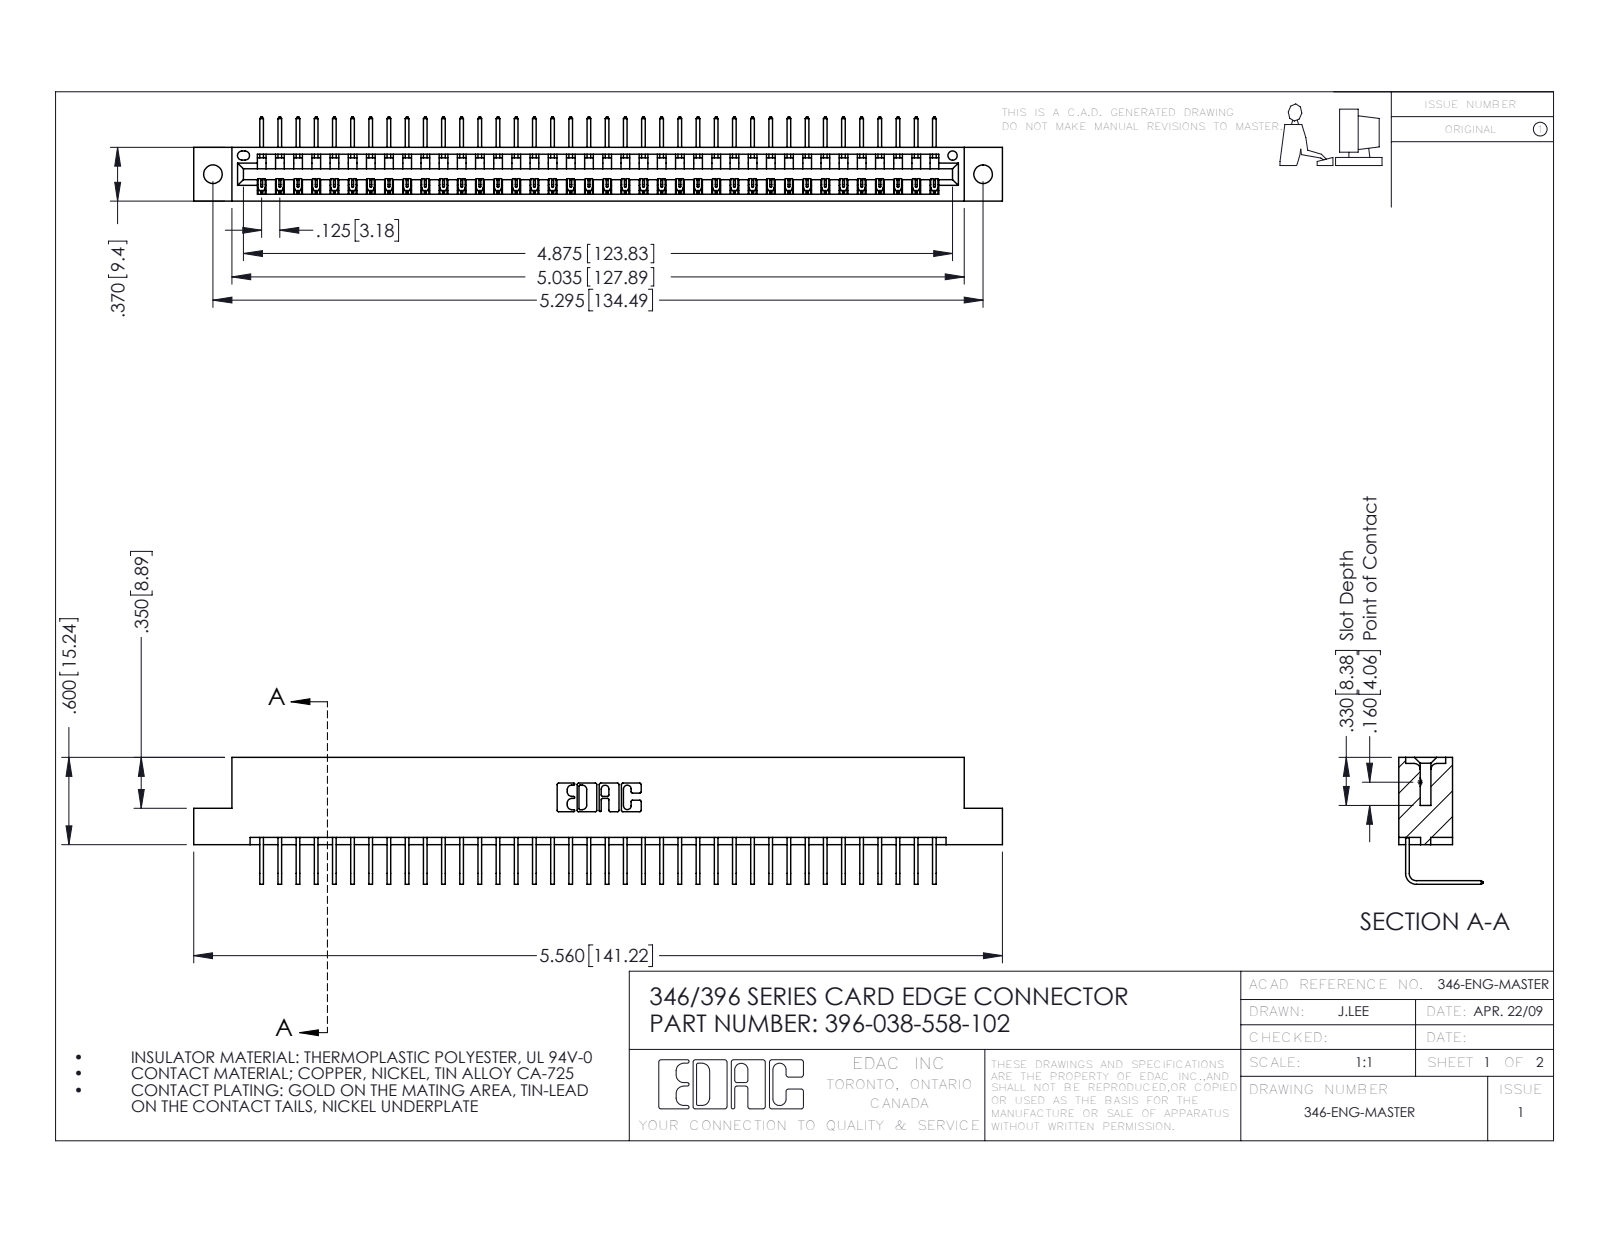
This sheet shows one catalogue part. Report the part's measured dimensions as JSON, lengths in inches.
{"part_name": "345-292-001_558 Tail - 2; 346 Part_Flush Mounting Lugs - 0.128 Dia; 396-038-558-102", "step_written_by": "SolidWorks 2016 (CONFIG_CONTROL_DESIGN)", "units": "inches", "bodies": {"solids": 39, "faces": 2402, "planar": 1672, "cylindrical": 730, "other": 0}, "overall_size": [5.56, 0.873, 0.58], "volume_in3": 0.829, "surface_area_in2": 26.99, "round_holes": [[0.128, 2], [0.064, 1]], "partial_cylinders_radius": [[0.006, 76], [0.01, 22], [0.007, 6], [0.031, 6], [0.026, 3], [0.031, 2], [0.04, 2], [0.014, 1]], "face_to_face_distances": [0.322, 0.048, 0.37, 0.25, 0.298, 0.025, 0.072, 0.148, 0.222, 0.1], "hole_center_spacings": [0.246, 5.086, 5.295]}
